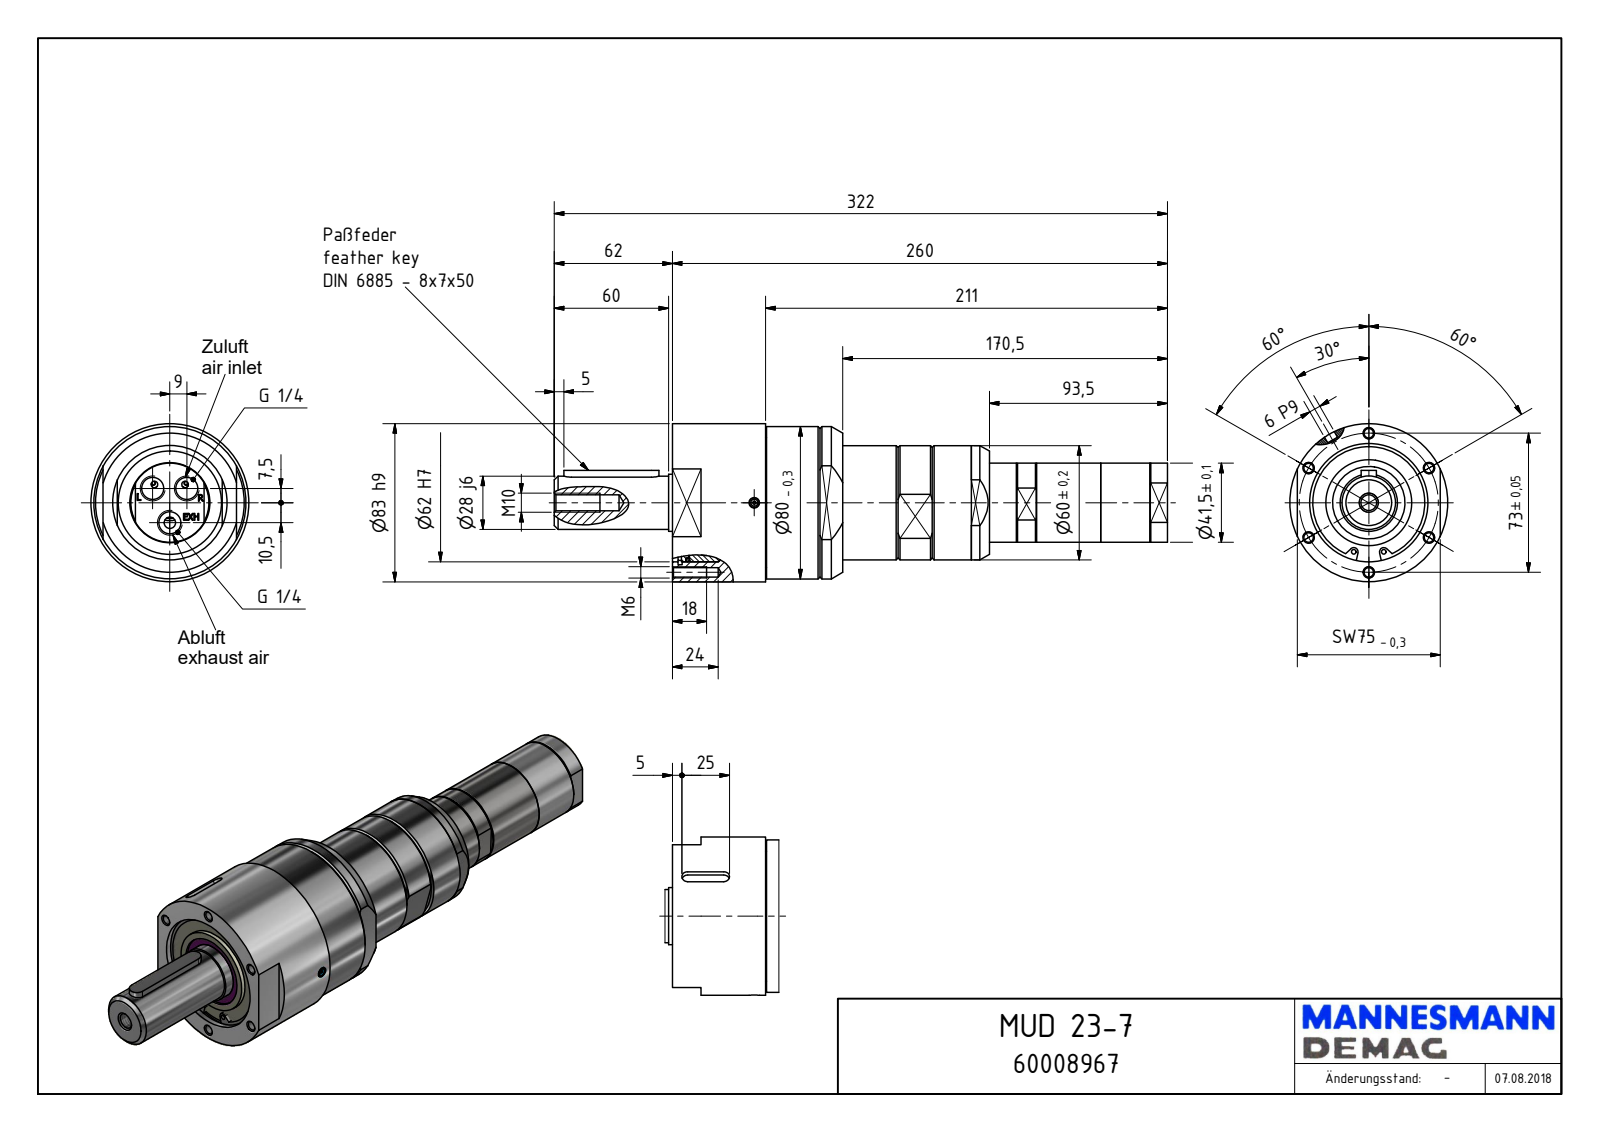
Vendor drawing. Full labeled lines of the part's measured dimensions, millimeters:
Part name (STEP PRODUCT): MUD 23-7_60008967
STEP written by: Autodesk Inventor 2018 (AUTOMOTIVE_DESIGN)
Units: millimetres
Bodies: 1 solid, 594 faces (239 planar, 281 cylindrical, 74 other)
Overall size (bounding box): 322 × 83 × 83
Volume: 819 574 mm³ · Surface area: 84 569 mm²
Round holes (diameter × count): ⌀4.92 ×6, ⌀1.55 ×3, ⌀11.45 ×3, ⌀2.5 ×2, ⌀4 ×2, ⌀5.5 ×2, ⌀8.38 ×1, ⌀36.5 ×1, ⌀38 ×1, ⌀40 ×1, ⌀42 ×1, ⌀58.69 ×1
Round bosses / shafts (diameter × count): ⌀5 ×2, ⌀3.6 ×2, ⌀3.3 ×2, ⌀83 ×1, ⌀80 ×1, ⌀68.18 ×1, ⌀60 ×1, ⌀45 ×1
Partial cylindrical surfaces — rounded edges, fillets, slot ends (radius × count): R3.5 ×100, R2.25 ×2, R3 ×2, R4 ×2, R10.7 ×2, R24.08 ×1, R24.96 ×1, R32.5 ×1
Main face-to-face distances: 49, 0.5, 89.5, 40.5, 2.5, 49.5, 40, 77, 4.8, 44.2
Hole centre spacings: 36.5, 63.22, 73, 11.72, 13.29, 17.21, 20.12, 24.9
